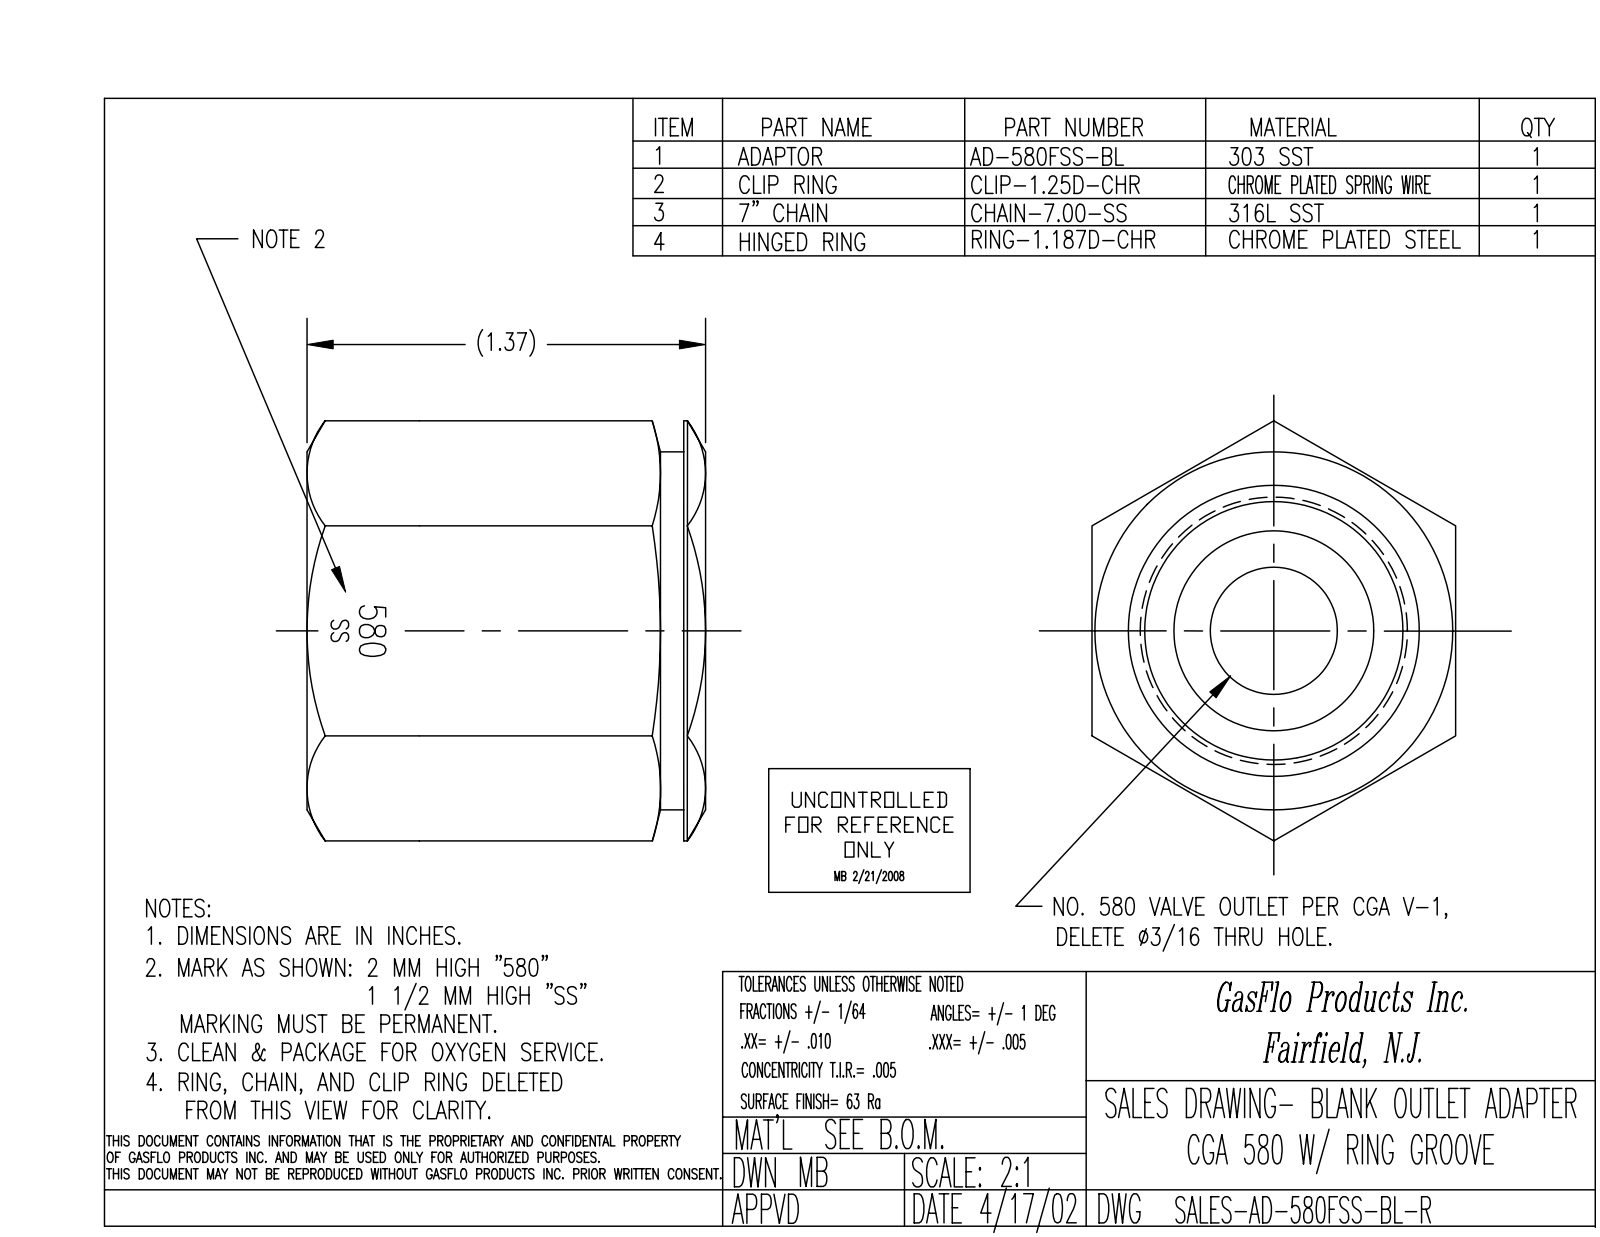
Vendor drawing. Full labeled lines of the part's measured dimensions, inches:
Part name (STEP PRODUCT): PRT-002239_STAINLESS; PRT-002245_RING-1.187D HALF; PRT-002255_SMALL PIN; AD-580FSS-BL-R (+4 more)
STEP written by: SolidWorks 2018 (CONFIG_CONTROL_DESIGN)
Units: inches
Bodies: 19 solids, 536 faces (86 planar, 180 cylindrical, 270 other)
Overall size (bounding box): 8.146 × 2.575 × 1.375
Volume: 1.422 in³ · Surface area: 19.22 in²
Round holes (diameter × count): ⌀0.063 ×1, ⌀0.422 ×1, ⌀0.892 ×1
Round bosses / shafts (diameter × count): ⌀0.063 ×58, ⌀1.243 ×1, ⌀0.1 ×1
Partial cylindrical surfaces — rounded edges, fillets, slot ends (radius × count): R0.005 ×24, R0.25 ×4, R0.01 ×2
Main face-to-face distances: 1.25, 1.25, 1.37, 0.683, 0.687, 1.298, 0.615, 0.072, 0.618, 0.632
